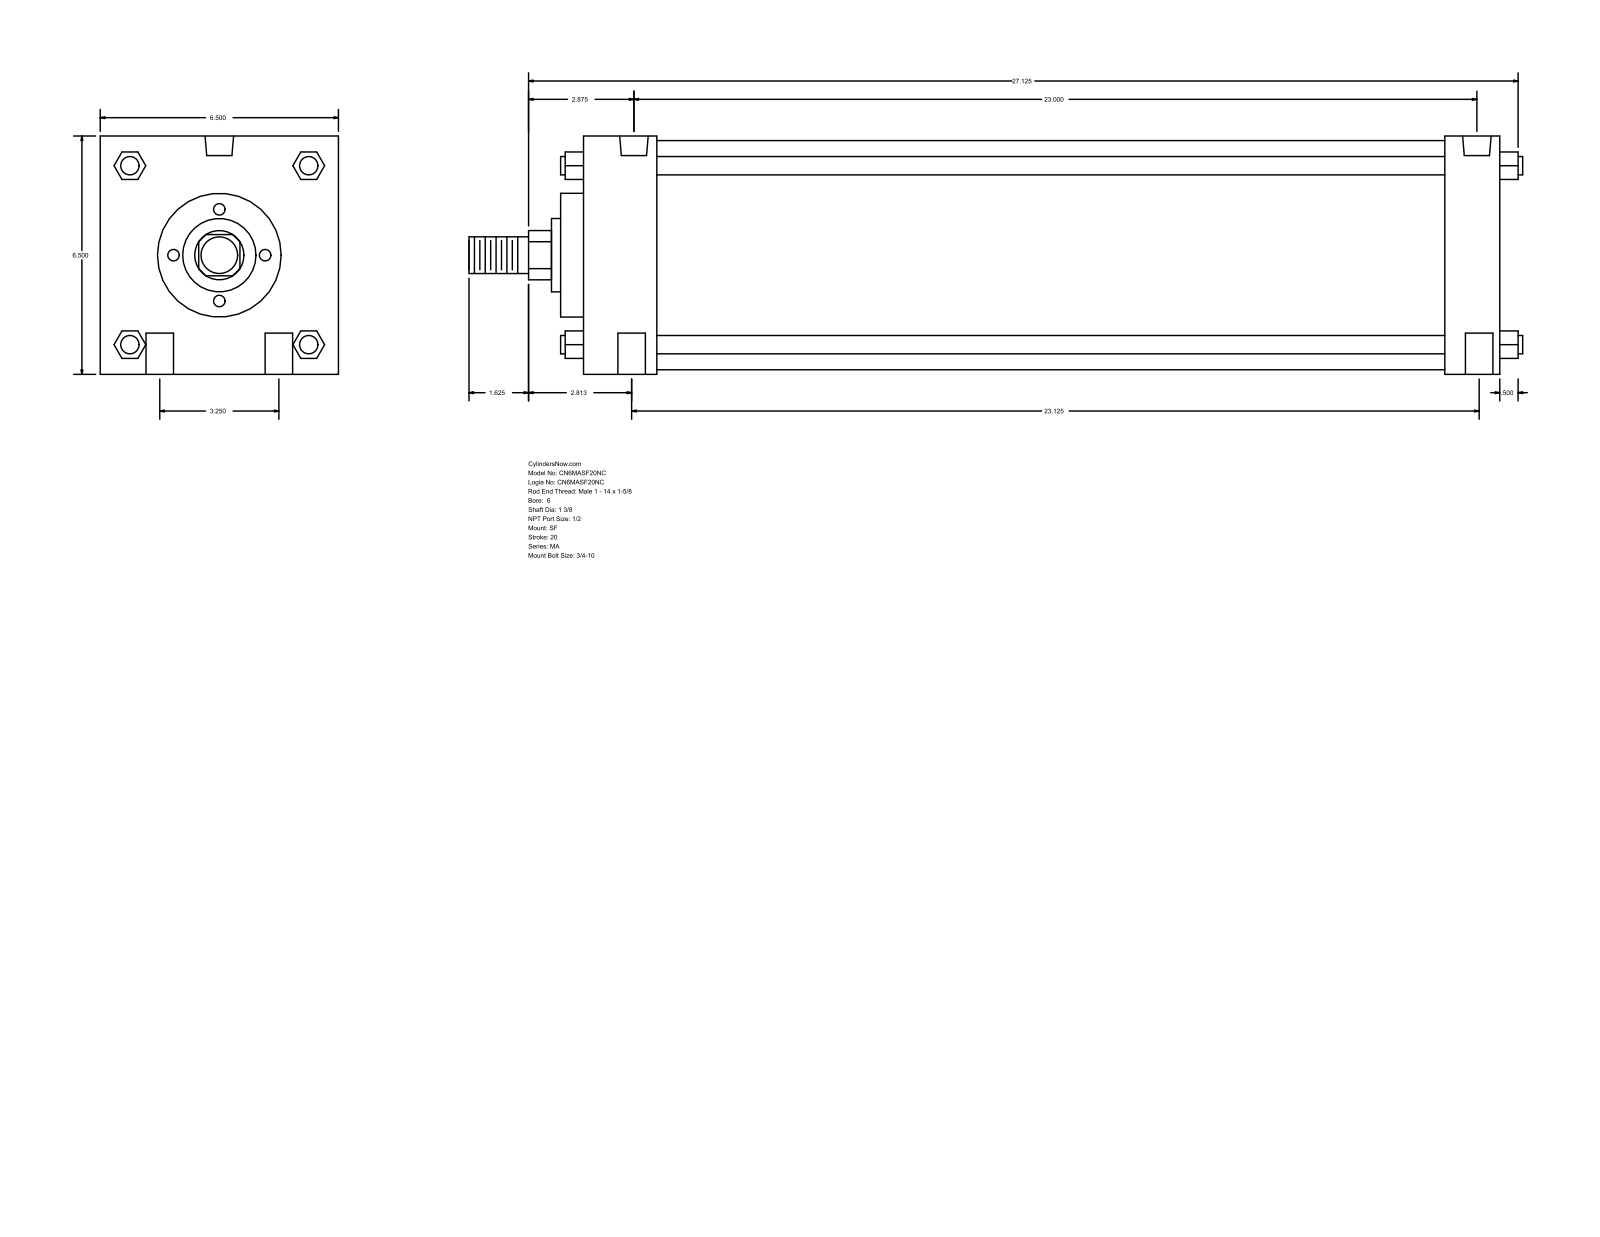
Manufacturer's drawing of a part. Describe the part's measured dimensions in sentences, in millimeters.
The part is named "MA_SF__0600_1.375". Its 3-D file was written by "GSSL Pune (CONFIG_CONTROL_DESIGN)". It is 0 solids with 126 faces: 95 planar, 31 cylindrical and 0 other. Overall it measures 730.25 by 165.1 by 165.1 millimeters. Round holes: 4 of diameter 19.05, 2 of diameter 17.46, 2 of diameter 19.77. Round bosses or shafts: 4 of diameter 12.7, 1 of diameter 158.75, 1 of diameter 85.72, 1 of diameter 50.8, 1 of diameter 34.92, 1 of diameter 25.4. Partial cylindrical surfaces (rounded edges, fillets, slot ends): 1 of radius 17.06. The main face-to-face distances are 165.1, 635, 596.9, 50.8, 38.1, 546.1, 584.2, 66.67, 15.87, 612.77. The hole center spacings are 41.3, 82.54, 584.2, 587.23, 587.24, 587.37, 593.14.
